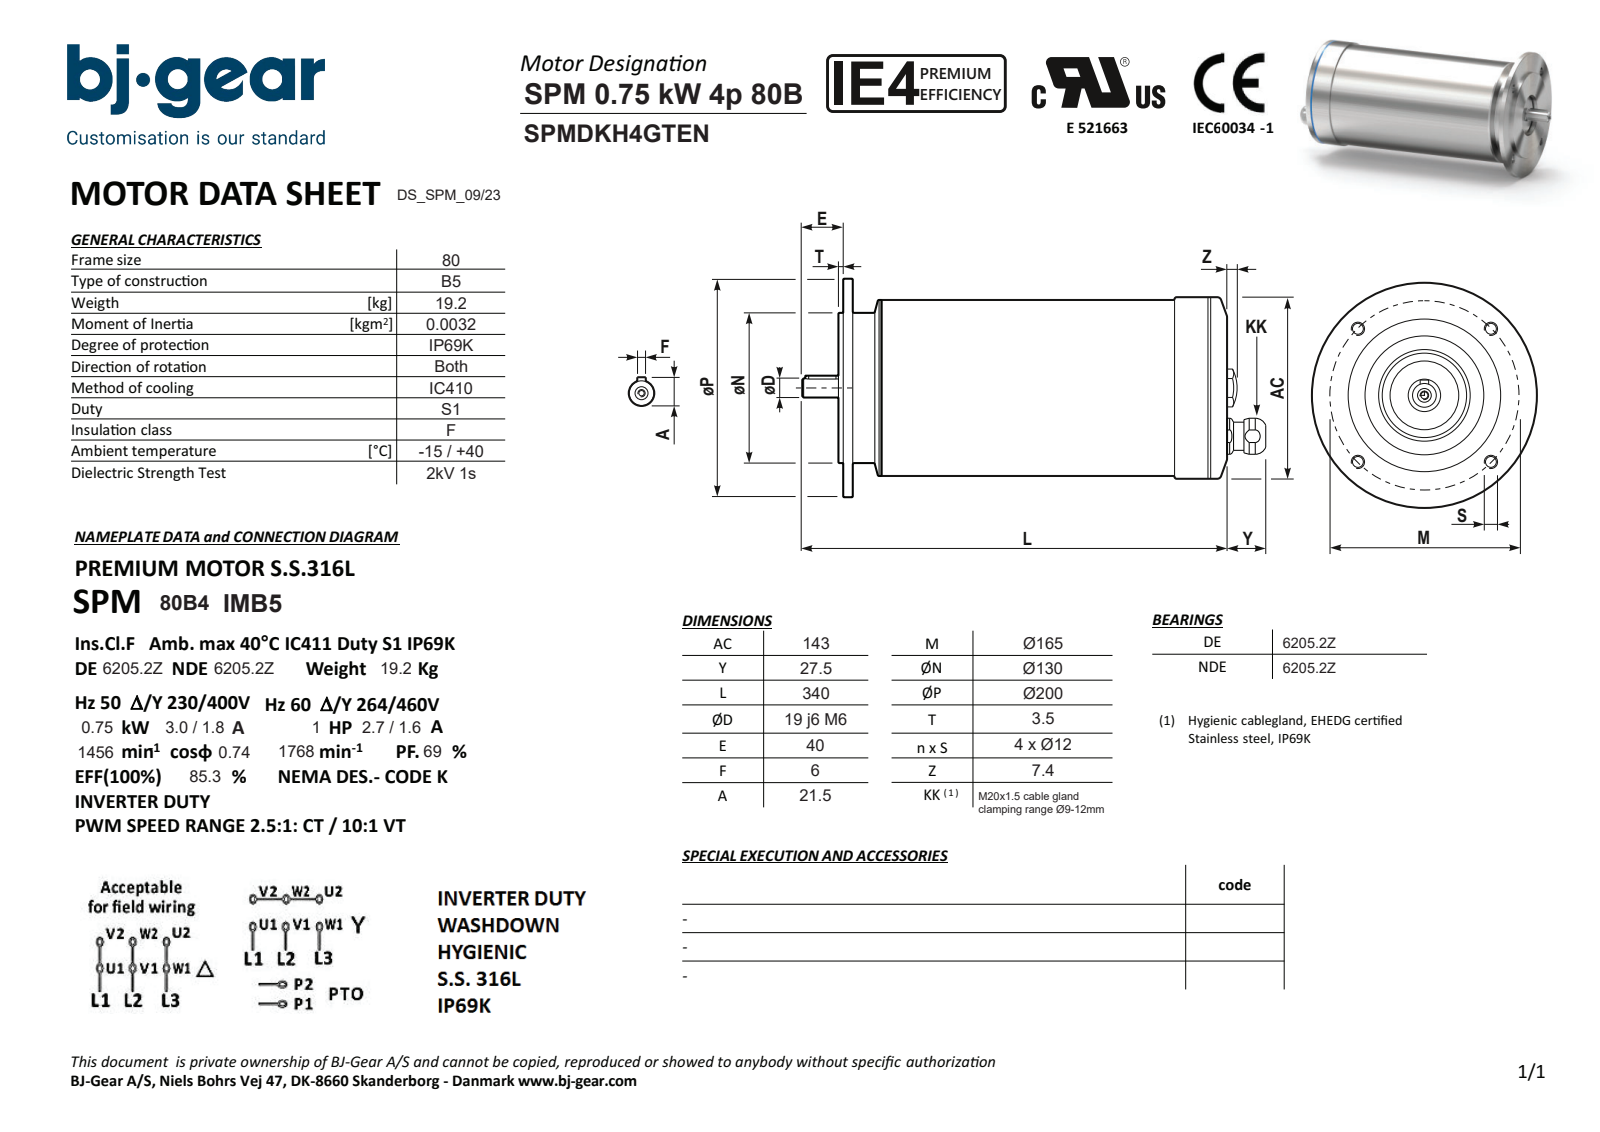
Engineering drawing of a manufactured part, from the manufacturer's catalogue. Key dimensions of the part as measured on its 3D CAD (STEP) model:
Part name (STEP PRODUCT): SPMDKH4GTENN4KSA1-N---NNN
STEP written by: Solid Edge (AUTOMOTIVE_DESIGN)
Units: millimetres
Bodies: 1 solid, 79 faces (30 planar, 28 cylindrical, 21 other)
Overall size (bounding box): 367.5 × 200 × 200
Volume: 4 736 000 mm³ · Surface area: 203 697 mm²
Round holes (diameter × count): ⌀12 ×4, ⌀4.92 ×1, ⌀6.4 ×1, ⌀7 ×1, ⌀13.4 ×1, ⌀68 ×1
Round bosses / shafts (diameter × count): ⌀200 ×1, ⌀143 ×1, ⌀142.98 ×1, ⌀139 ×1, ⌀138.98 ×1, ⌀130 ×1, ⌀25 ×1, ⌀20 ×1
Partial cylindrical surfaces — rounded edges, fillets, slot ends (radius × count): R3 ×2, R12.8 ×1
Main face-to-face distances: 8, 11.5, 3.5, 292, 300, 303.5, 6, 2, 294, 9.5
Hole centre spacings: 82.51, 116.68, 61.78, 112.63, 165.01, 38
